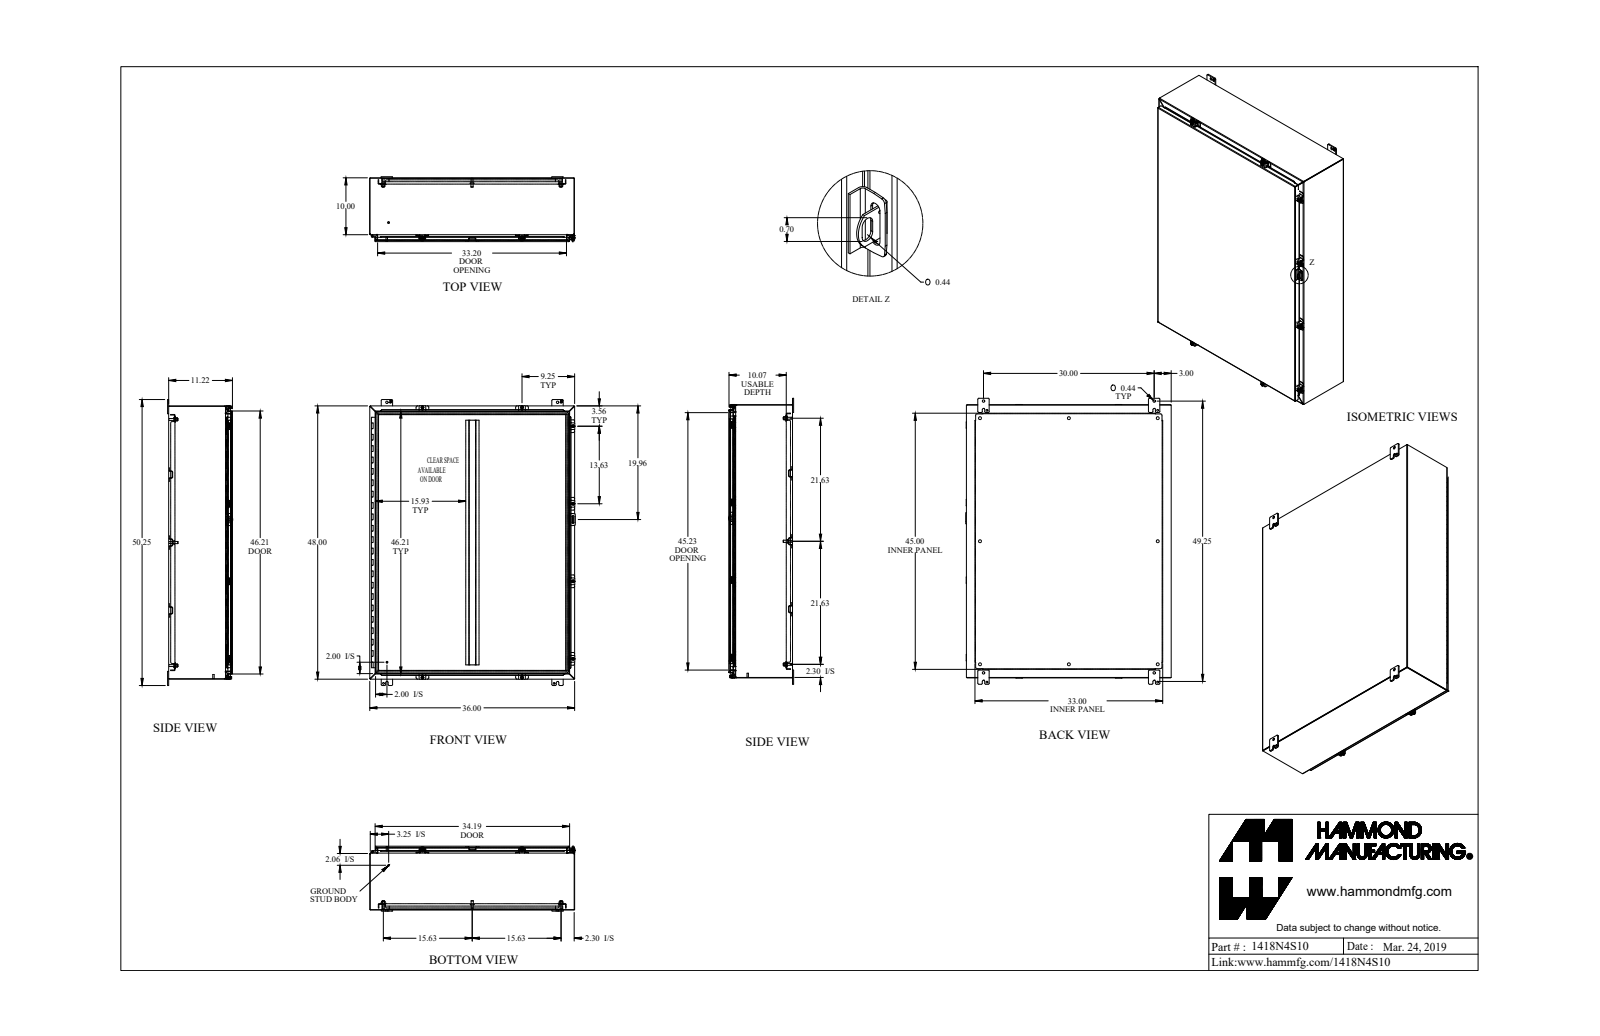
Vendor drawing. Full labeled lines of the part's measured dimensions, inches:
Part name (STEP PRODUCT): 1418N4S10_Default
STEP written by: SolidWorks 2019 (CONFIG_CONTROL_DESIGN)
Units: inches
Bodies: 69 solids, 2398 faces (1397 planar, 869 cylindrical, 132 other)
Overall size (bounding box): 50.25 × 36.125 × 11.437
Volume: 607.5 in³ · Surface area: 15 853 in²
Round holes (diameter × count): ⌀0.213 ×8, ⌀0.265 ×8, ⌀0.375 ×8, ⌀0.5 ×8, ⌀0.307 ×4, ⌀0.313 ×4, ⌀0.437 ×4, ⌀0.445 ×4, ⌀0.125 ×1, ⌀0.187 ×1
Round bosses / shafts (diameter × count): ⌀0.65 ×8, ⌀0.5 ×8, ⌀0.39 ×8, ⌀0.375 ×8, ⌀0.33 ×8, ⌀0.244 ×8, ⌀1 ×4, ⌀0.281 ×2
Partial cylindrical surfaces — rounded edges, fillets, slot ends (radius × count): R0.25 ×48, R0.048 ×39, R0.143 ×39, R0.188 ×39, R0.036 ×22, R0.108 ×22, R0.116 ×16, R0.141 ×16
Main face-to-face distances: 0.072, 11.143, 11.071, 11.215, 0.095, 0.937, 1.009, 10.111, 10.039, 1.032
Hole centre spacings: 38.003, 7.196, 15.625, 24.468, 43.25, 45.986, 51.507, 21.625
